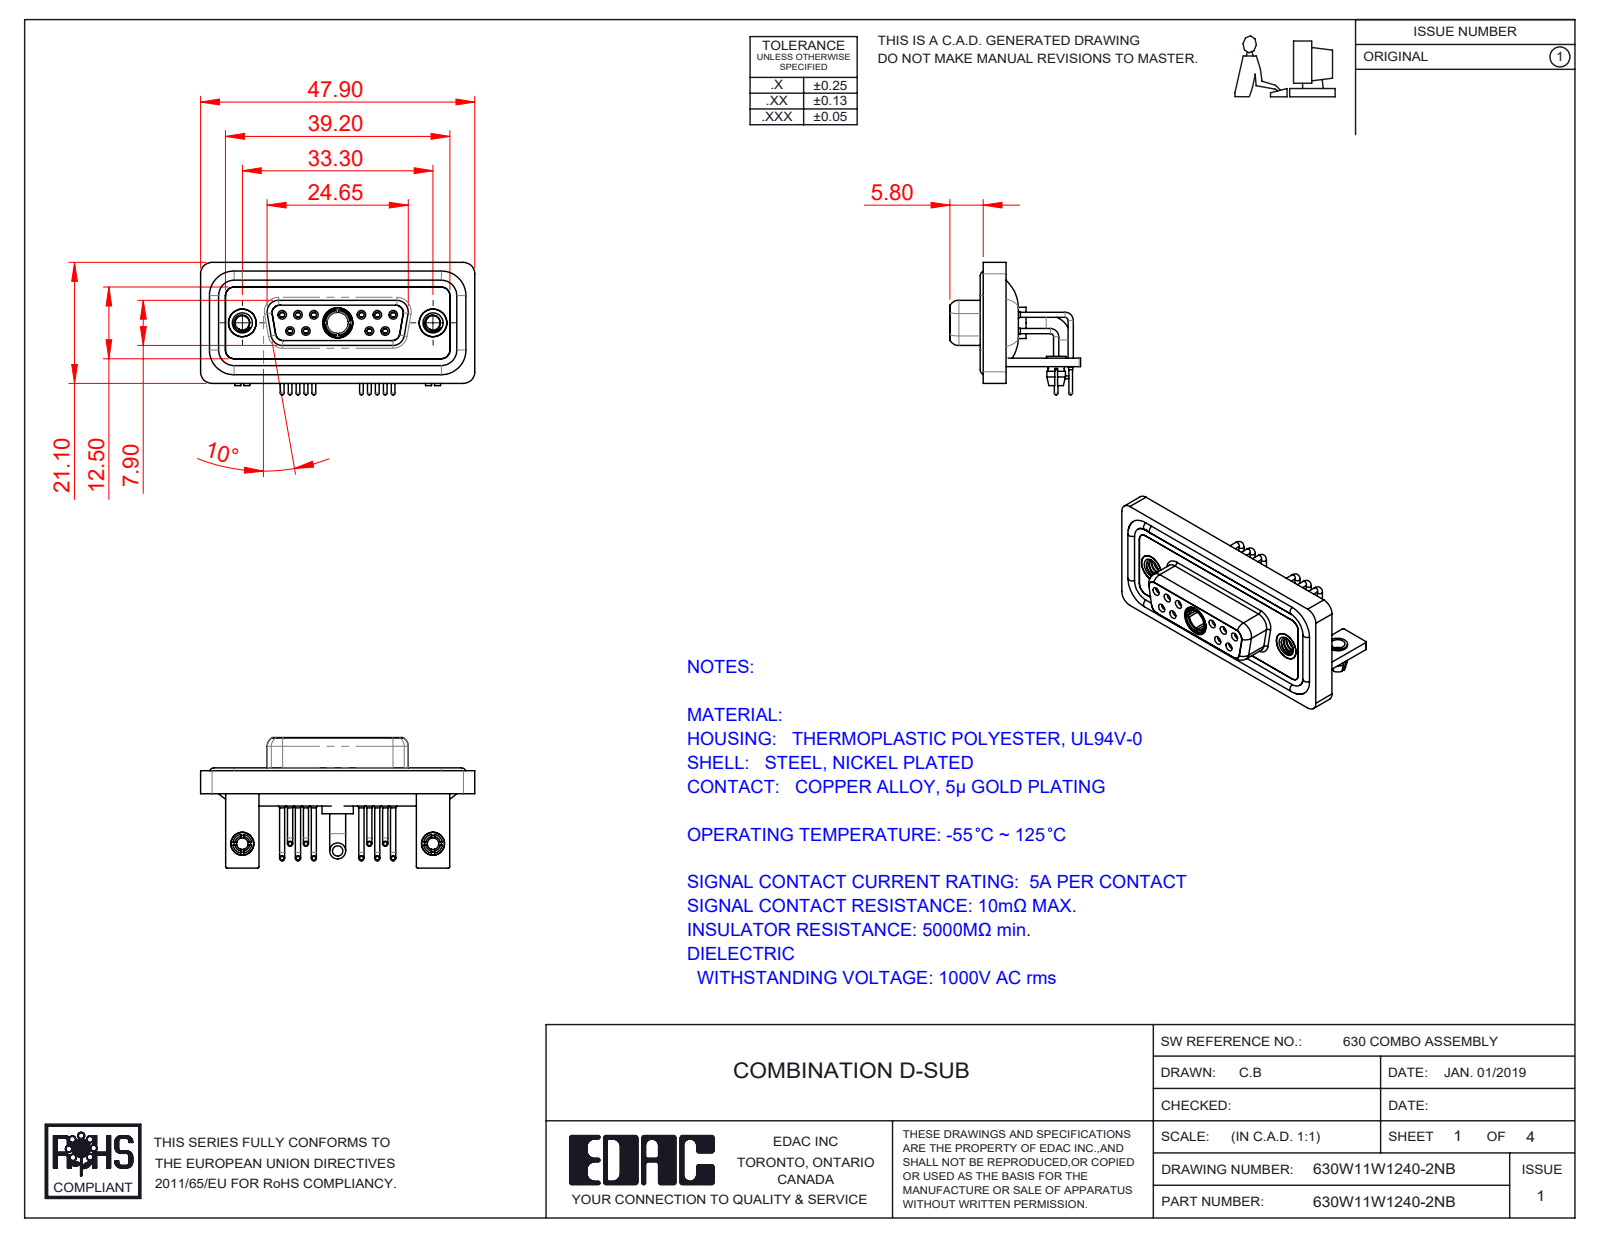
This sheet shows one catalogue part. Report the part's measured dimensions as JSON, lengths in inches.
{"part_name": "630Combo Board Lock_50 Contacts; 630Combo Contact Row 2_50 Contacts; 630Combo Shell Rear_15 Contacts; 630Combo Shell Front_15 Contacts (+7 more)", "step_written_by": "SolidWorks 2020 (CONFIG_CONTROL_DESIGN)", "units": "inches", "bodies": {"solids": 23, "faces": 1128, "planar": 352, "cylindrical": 497, "other": 279}, "overall_size": [1.886, 0.91, 0.898], "volume_in3": 0.404, "surface_area_in2": 17.7, "round_holes": [[0.079, 12], [0.035, 10], [0.043, 10], [0.059, 10], [0.067, 6], [0.063, 4], [0.098, 4], [0.191, 3], [0.126, 2], [0.157, 2], [0.159, 2], [0.197, 2]], "round_bosses_or_shafts": [[0.063, 10], [0.035, 10], [0.026, 10], [0.195, 2], [0.189, 2], [0.157, 2], [0.134, 2], [0.13, 2]], "partial_cylinders_radius": [[0.079, 21], [0.059, 18], [0.01, 16], [0.053, 12], [0.063, 8], [0.02, 5], [0.024, 4], [0.026, 4]], "face_to_face_distances": [0.016, 0.114, 0.059, 0.071, 0.146, 0.043, 0.063, 0.161, 0.031, 0.098], "hole_center_spacings": [0.124, 0.109, 0.545, 0.436, 0.654, 0.198, 0.198, 0.218]}
